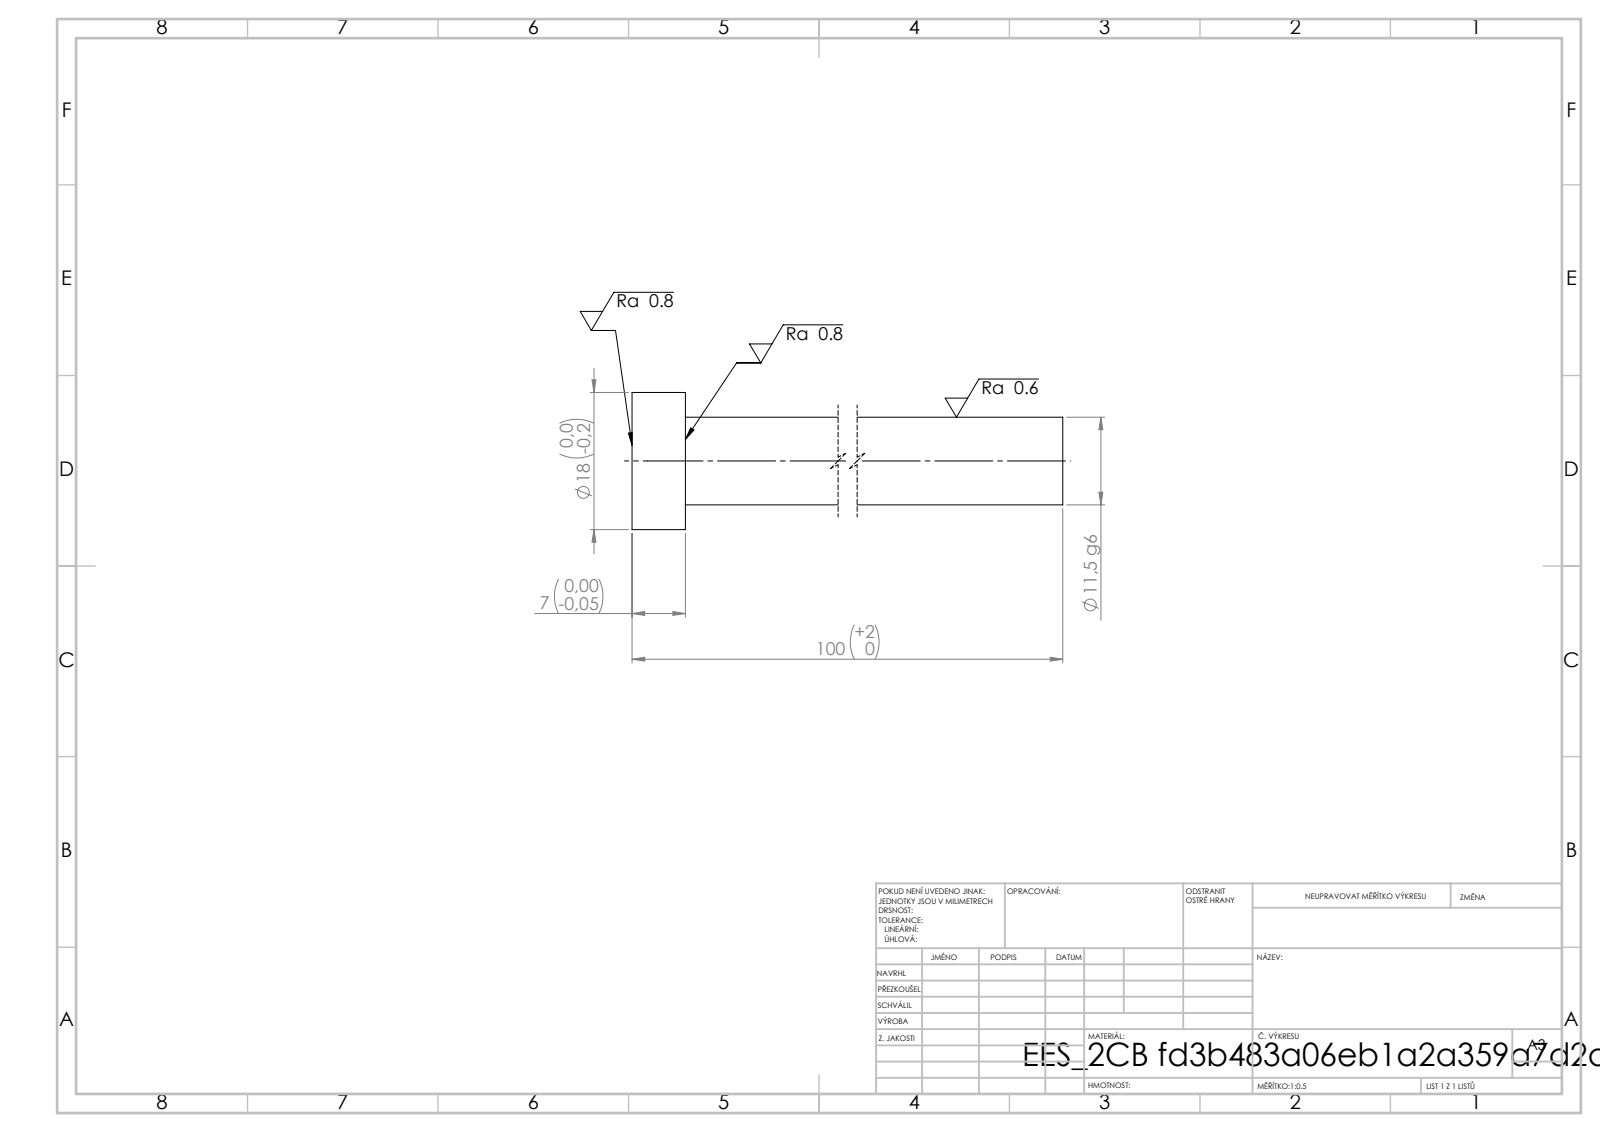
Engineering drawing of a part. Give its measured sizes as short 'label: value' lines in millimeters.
written by: SolidWorks 2019 (CONFIG_CONTROL_DESIGN)
unit: mm
bodies: 1 solid, 7 faces (3 planar, 4 cylindrical, 0 other)
size: 100 × 18 × 18
volume: 11 441 mm³; area: 4 265 mm²
bosses: 1× ⌀18, 1× ⌀11.5
face distances: 7, 100, 93
